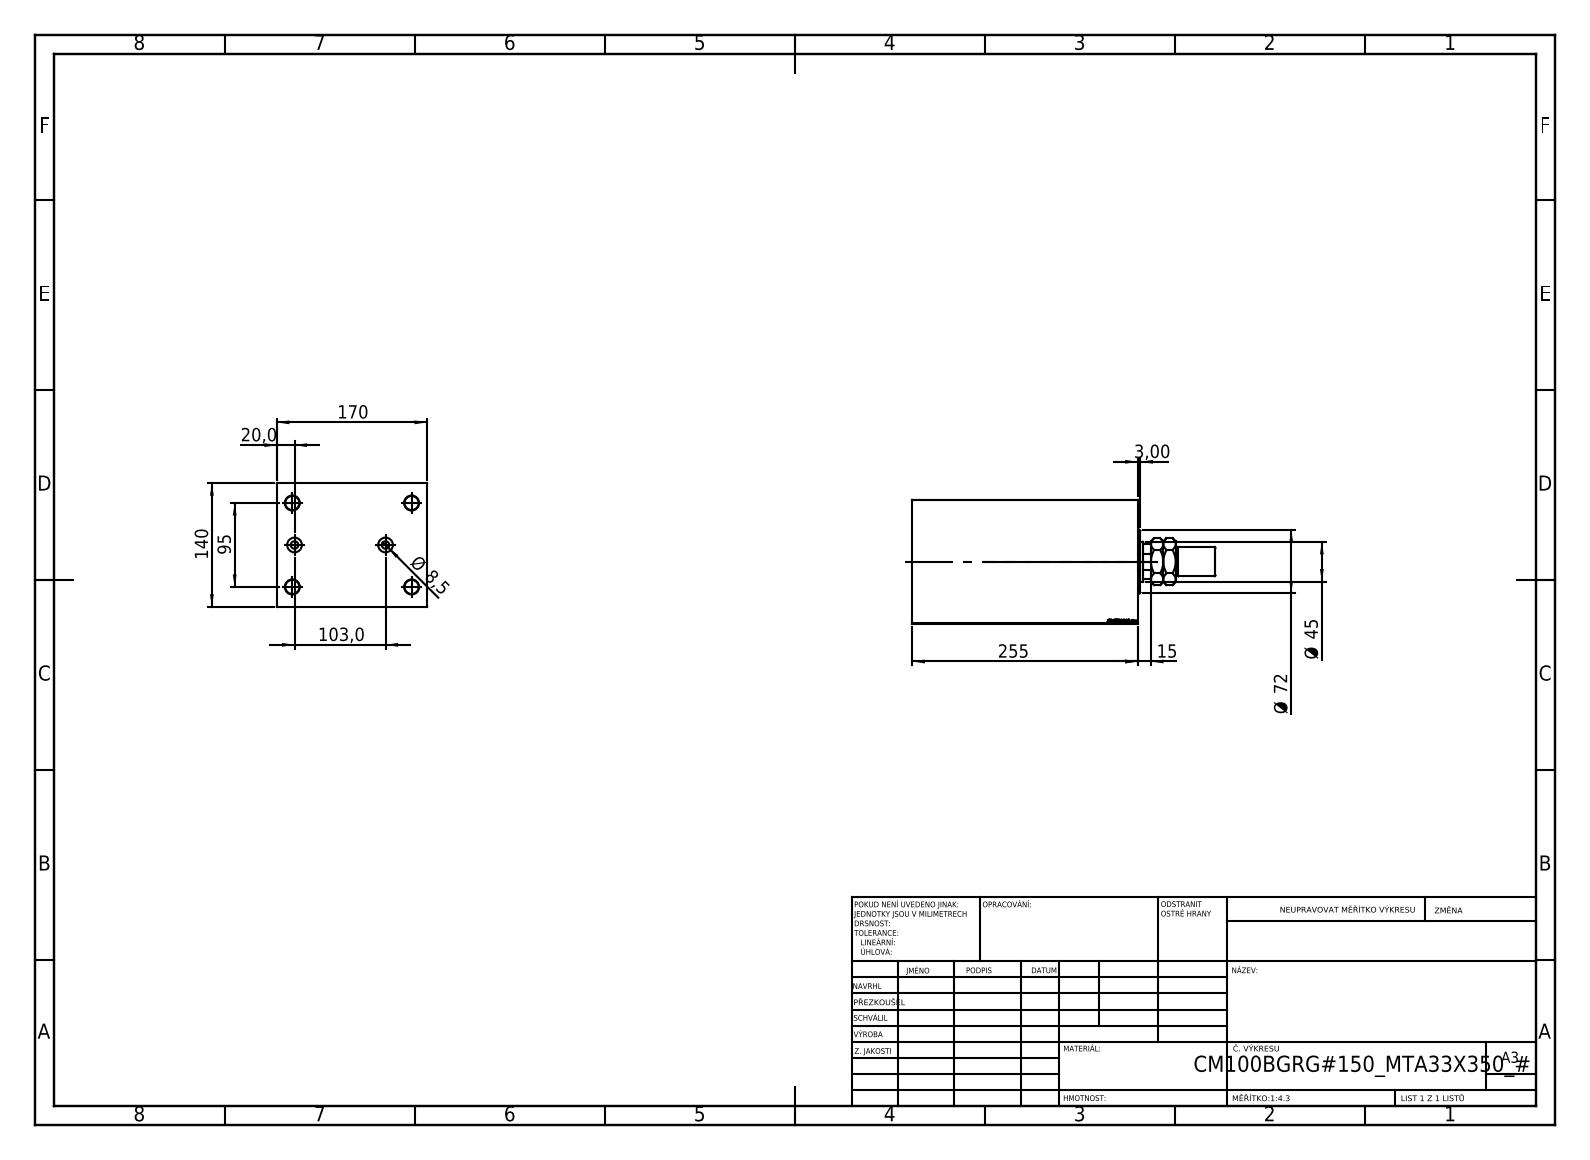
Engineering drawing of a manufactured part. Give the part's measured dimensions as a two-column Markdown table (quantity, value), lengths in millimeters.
| quantity | value |
| --- | --- |
| part name | V450CM_B_VCP; V450CM_B_Body; V450CM_VC_B; MTA |
| STEP written by | SolidWorks 2019 (CONFIG_CONTROL_DESIGN) |
| units | millimeters |
| bodies | 4 solids, 928 faces (416 planar, 56 cylindrical, 456 other) |
| overall size | 343 × 170 × 140 |
| volume | 5 145 000 mm³ |
| surface area | 397 220 mm² |
| round holes (diameter × count) | 16 × 4, 8.5 × 2, 16.66 × 2, 31.5 × 1, 45 × 1, 48.5 × 1, 49.5 × 1, 100 × 1, 102 × 1, 105 × 1 |
| round bosses / shafts (diameter × count) | 72 × 1, 33 × 1, 31 × 1 |
| partial cylindrical surfaces (radius × count) | 22 × 1 |
| main face-to-face distances | 140, 170, 255, 229, 26, 15, 240, 214, 90, 64 |
| hole center spacings | 82.54, 47.57, 55.92, 95, 115.7, 135, 140.76, 165.08 |
